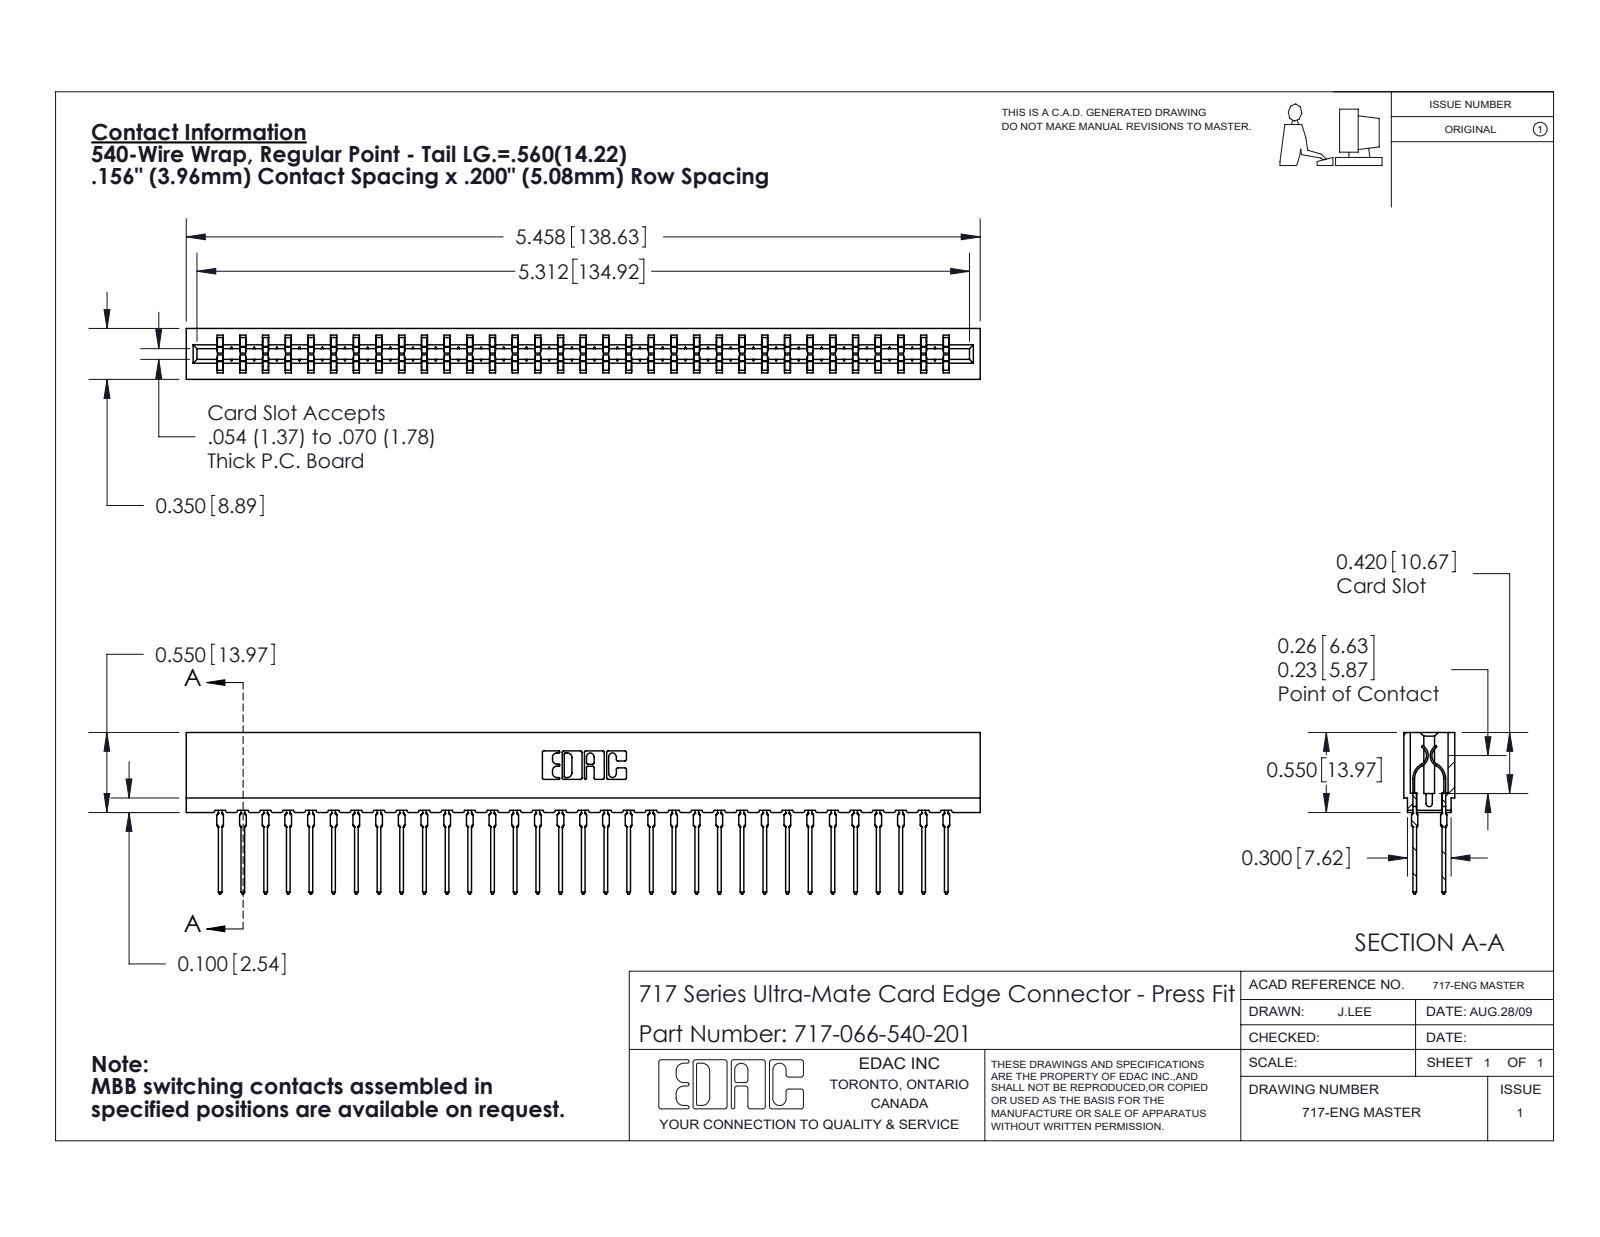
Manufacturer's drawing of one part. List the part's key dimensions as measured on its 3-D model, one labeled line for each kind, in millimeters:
Part name (STEP PRODUCT): 745-292-001_540; 717 Part_Insulator Option - 06; 717-066-540-201
STEP written by: SolidWorks 2020 (CONFIG_CONTROL_DESIGN)
Units: millimetres
Bodies: 67 solids, 6034 faces (3123 planar, 1195 cylindrical, 1716 other)
Overall size (bounding box): 138.6 × 28.2 × 8.9
Volume: 12 200 mm³ · Surface area: 19 460 mm²
Partial cylindrical surfaces — rounded edges, fillets, slot ends (radius × count): R0.5 ×132, R0.4 ×66, R0.3 ×22, R0.1 ×8, R0.3 ×8, R0.2 ×6, R0.8 ×6, R0.7 ×3
Main face-to-face distances: 5.4, 3.5, 8.9, 1.6, 7.3, 1.9, 3.8, 1.9, 2.2, 6.7
